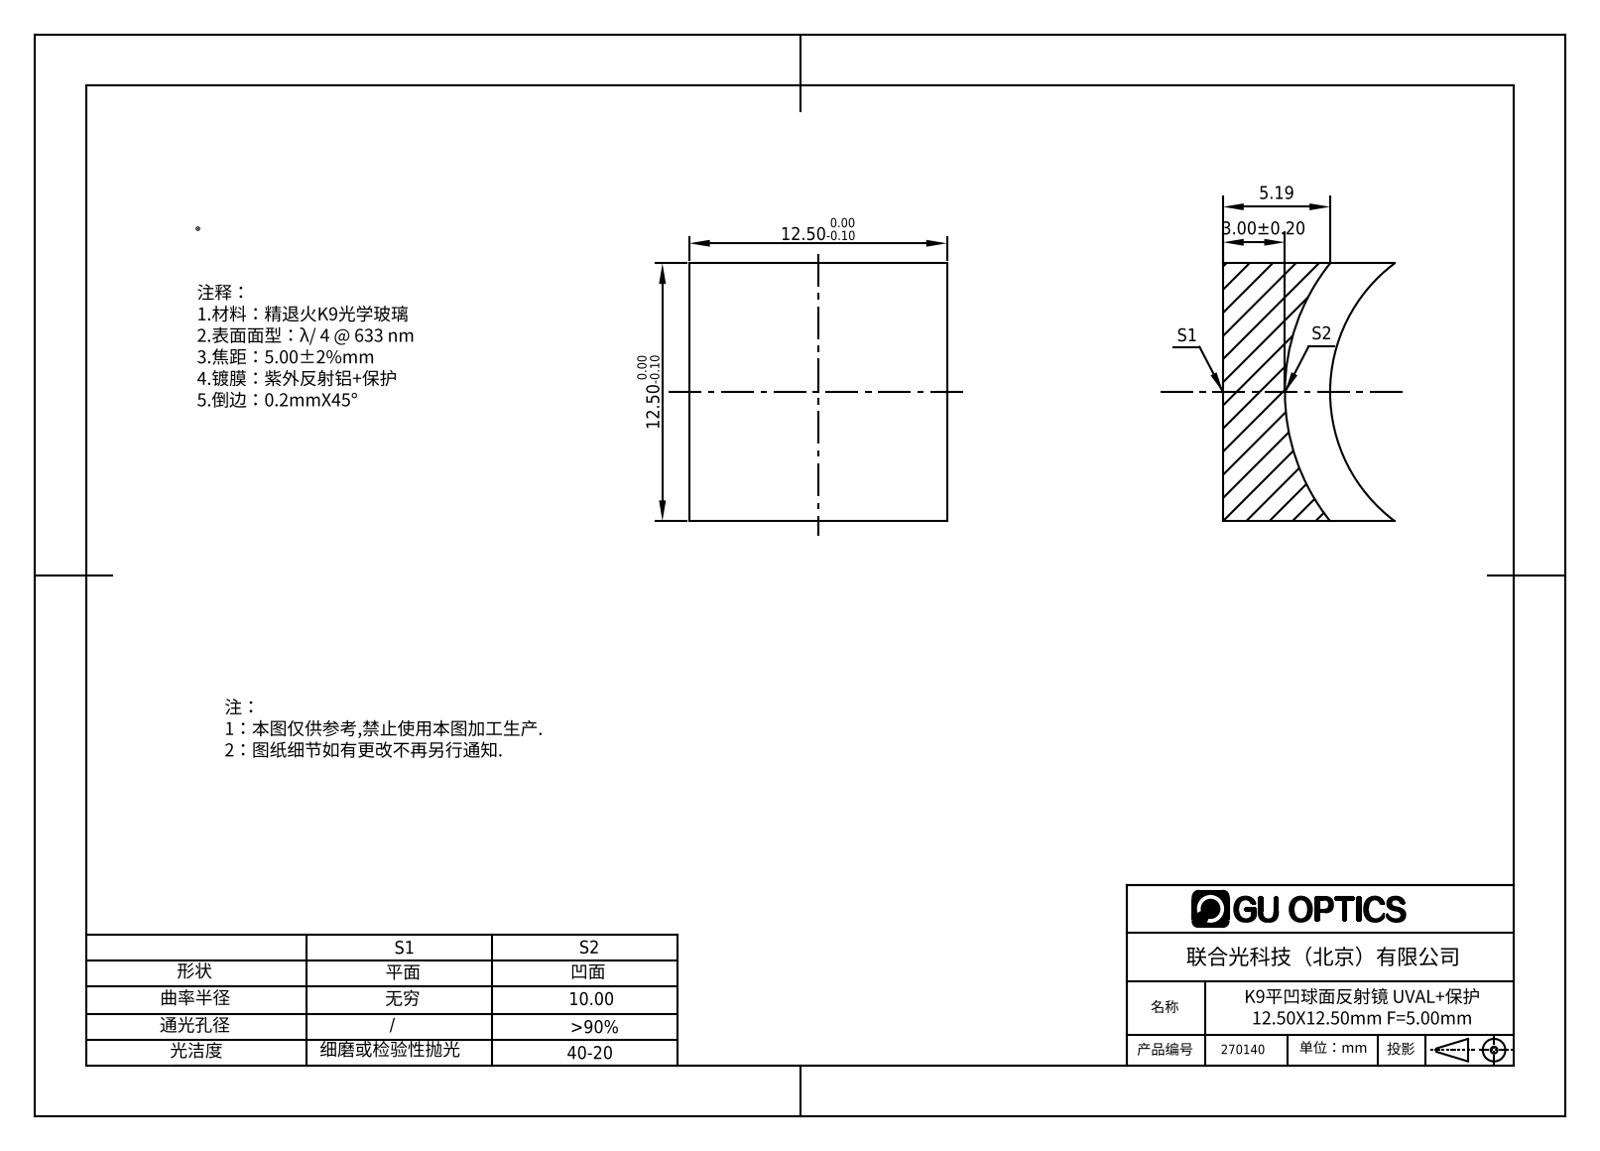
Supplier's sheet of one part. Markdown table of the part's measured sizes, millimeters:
| quantity | value |
| --- | --- |
| part name | 270010 |
| STEP written by | SolidWorks 2019 (AUTOMOTIVE_DESIGN) |
| units | millimeters |
| bodies | 1 solid, 7 faces (5 planar, 0 cylindrical, 2 other) |
| overall size | 12.5 × 12.5 × 8.32 |
| volume | 697 mm³ |
| surface area | 649 mm² |
| main face-to-face distances | 12.5 |
